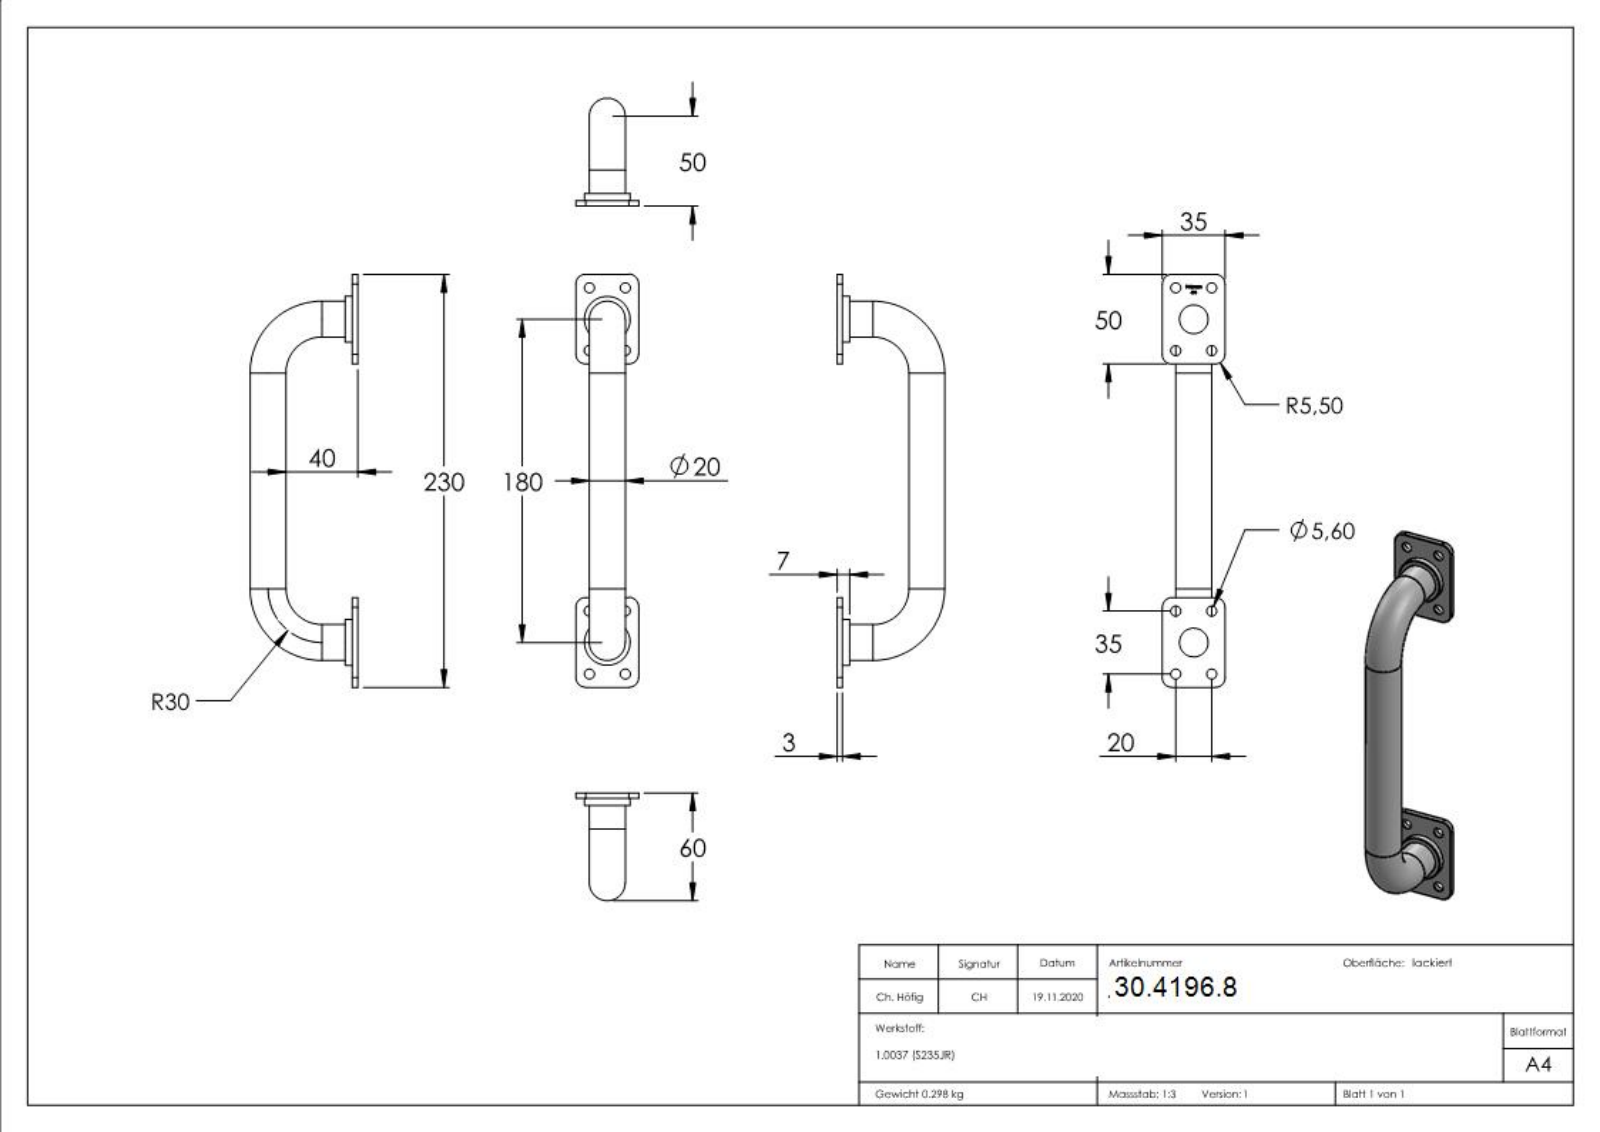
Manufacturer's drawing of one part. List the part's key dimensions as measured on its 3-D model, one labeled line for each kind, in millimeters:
Part name (STEP PRODUCT): 490
STEP written by: SolidWorks 2018 (CONFIG_CONTROL_DESIGN)
Units: millimetres
Bodies: 1 solid, 215 faces (101 planar, 40 cylindrical, 74 other)
Overall size (bounding box): 230 × 60 × 35
Volume: 38 195 mm³ · Surface area: 35 380 mm²
Round holes (diameter × count): ⌀5.6 ×8, ⌀16 ×3
Round bosses / shafts (diameter × count): ⌀20 ×3, ⌀25.5 ×2
Partial cylindrical surfaces — rounded edges, fillets, slot ends (radius × count): R5.5 ×8
Main face-to-face distances: 3, 7, 4, 35, 50, 180, 230, 130, 2.9, 6.9
Hole centre spacings: 20.16, 180, 20, 35, 40.31, 162.81, 181.11, 197.75
